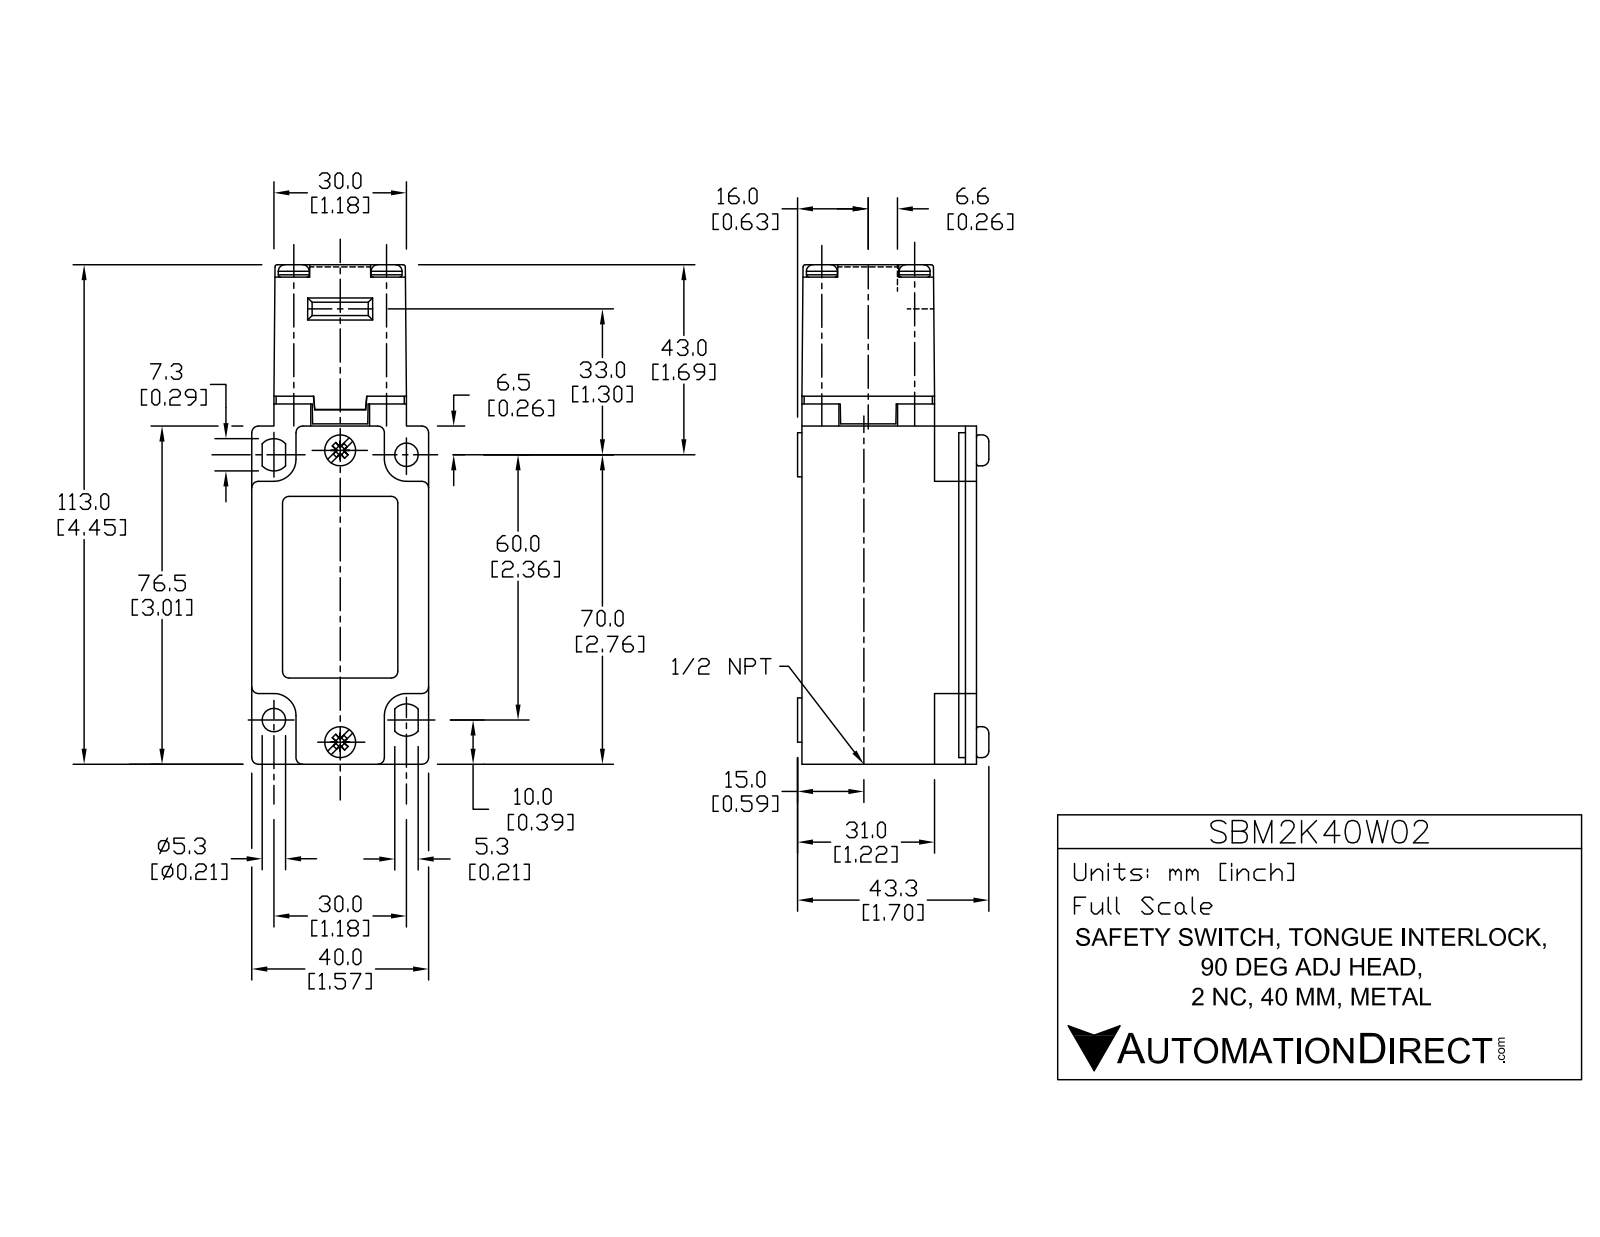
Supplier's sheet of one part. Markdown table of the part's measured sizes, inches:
| quantity | value |
| --- | --- |
| part name | SBM2K40W02 |
| STEP written by | SolidWorks 2017 (AUTOMOTIVE_DESIGN) |
| units | inches |
| bodies | 2 solids, 183 faces (97 planar, 72 cylindrical, 14 other) |
| overall size | 4.449 × 1.705 × 1.575 |
| volume | 8.506 in³ |
| surface area | 40.95 in² |
| round holes (diameter × count) | 0.205 × 2, 0.276 × 2, 0.669 × 1, 0.748 × 1 |
| round bosses / shafts (diameter × count) | 0.394 × 4, 0.276 × 4 |
| partial cylindrical surfaces (radius × count) | 0.059 × 16, 0.02 × 4, 0.197 × 4, 0.128 × 2, 0.453 × 1, 0.472 × 1 |
| main face-to-face distances | 1.181, 0.197, 1.575, 1.555, 1.378, 0.374, 3.012, 0.118, 0.02, 0.984 |
| hole center spacings | 0.557, 0.827, 2.641 |
